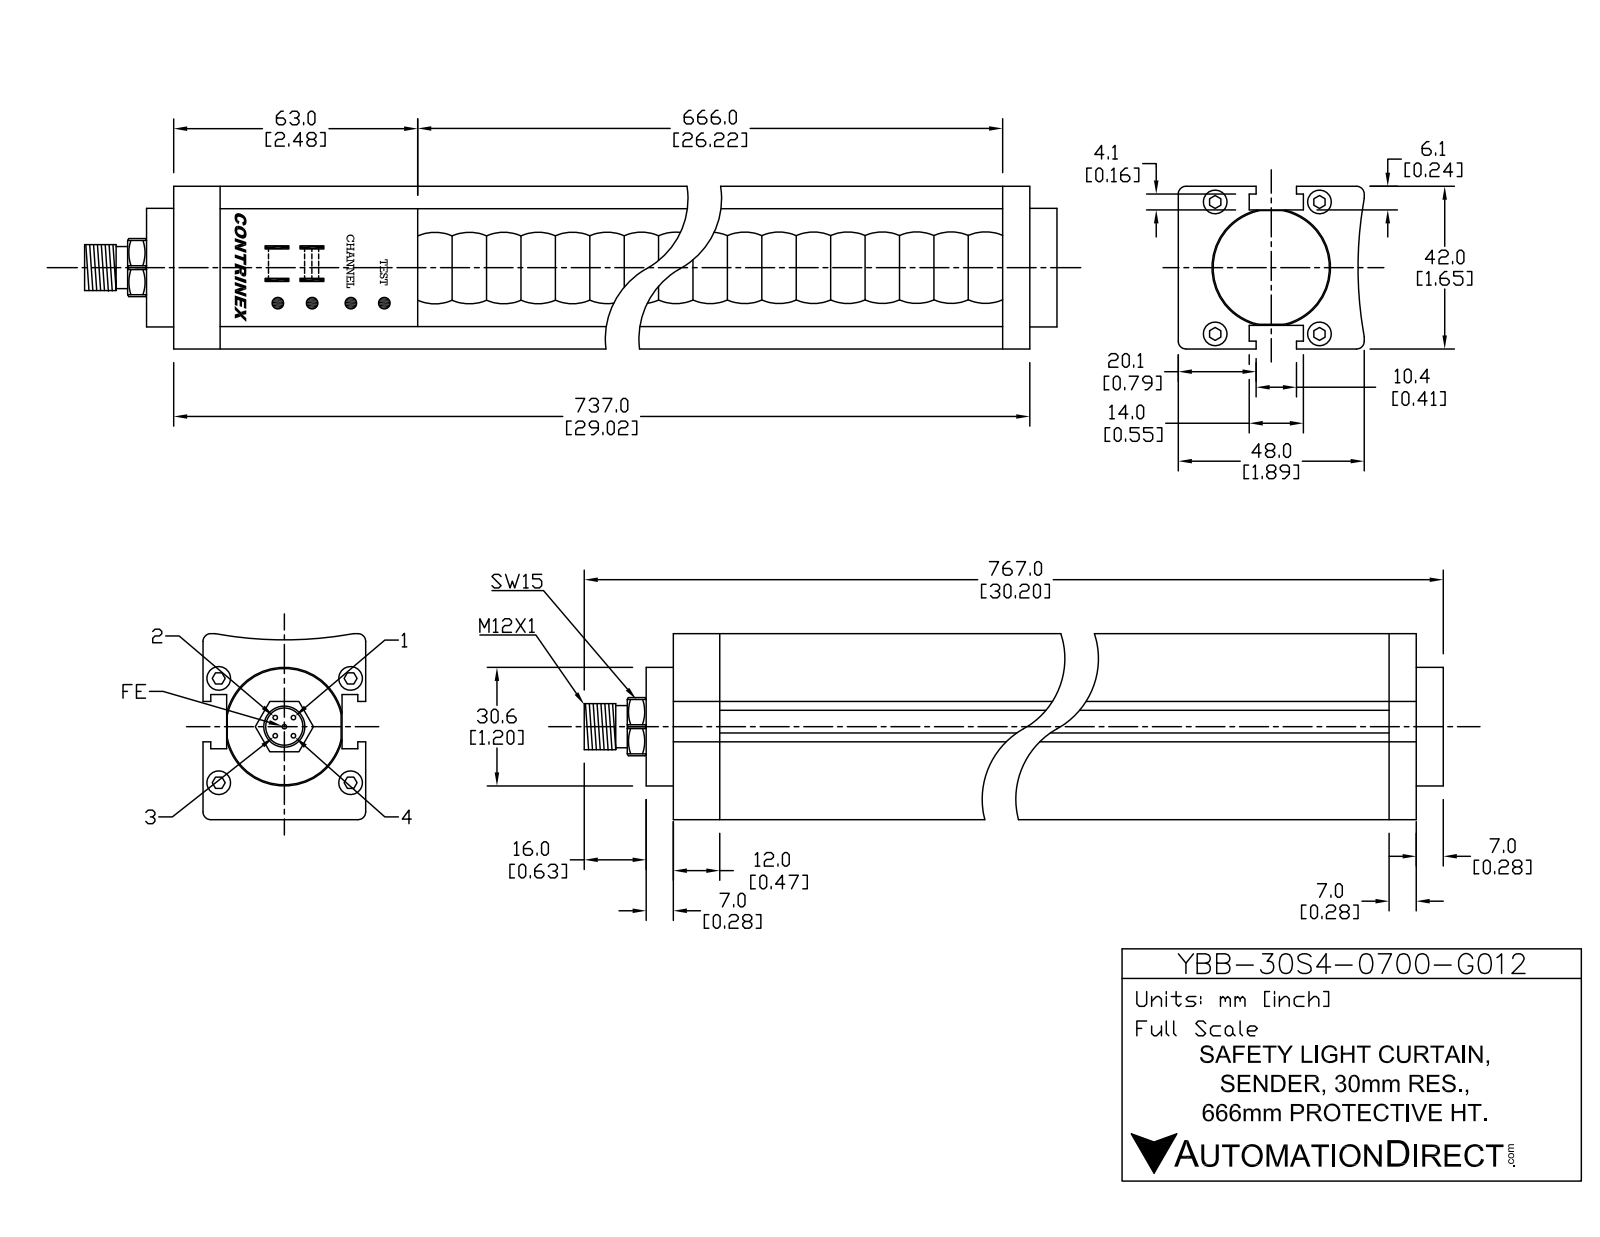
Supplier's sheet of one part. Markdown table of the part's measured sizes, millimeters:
| quantity | value |
| --- | --- |
| part name | YBB-30S4-0700-G012 |
| STEP written by | SolidWorks 2016 (AUTOMOTIVE_DESIGN) |
| units | millimeters |
| bodies | 19 solids, 440 faces (208 planar, 168 cylindrical, 64 other) |
| overall size | 767 × 48 × 42 |
| volume | 1 330 000 mm³ |
| surface area | 174 916 mm² |
| round holes (diameter × count) | 6 × 4, 8.5 × 1, 32 × 1 |
| round bosses / shafts (diameter × count) | 1 × 5, 5.5 × 4, 30.6 × 1, 12 × 1, 10.5 × 1 |
| partial cylindrical surfaces (radius × count) | 1 × 48, 0.5 × 4, 0.55 × 2, 8.2 × 1, 100 × 1 |
| main face-to-face distances | 6.3, 35.7, 42, 29.4, 14, 17.2, 31.2, 15.7, 29.7, 46.9 |
| hole center spacings | 21.04, 22.34, 26.9, 34, 43.35 |
